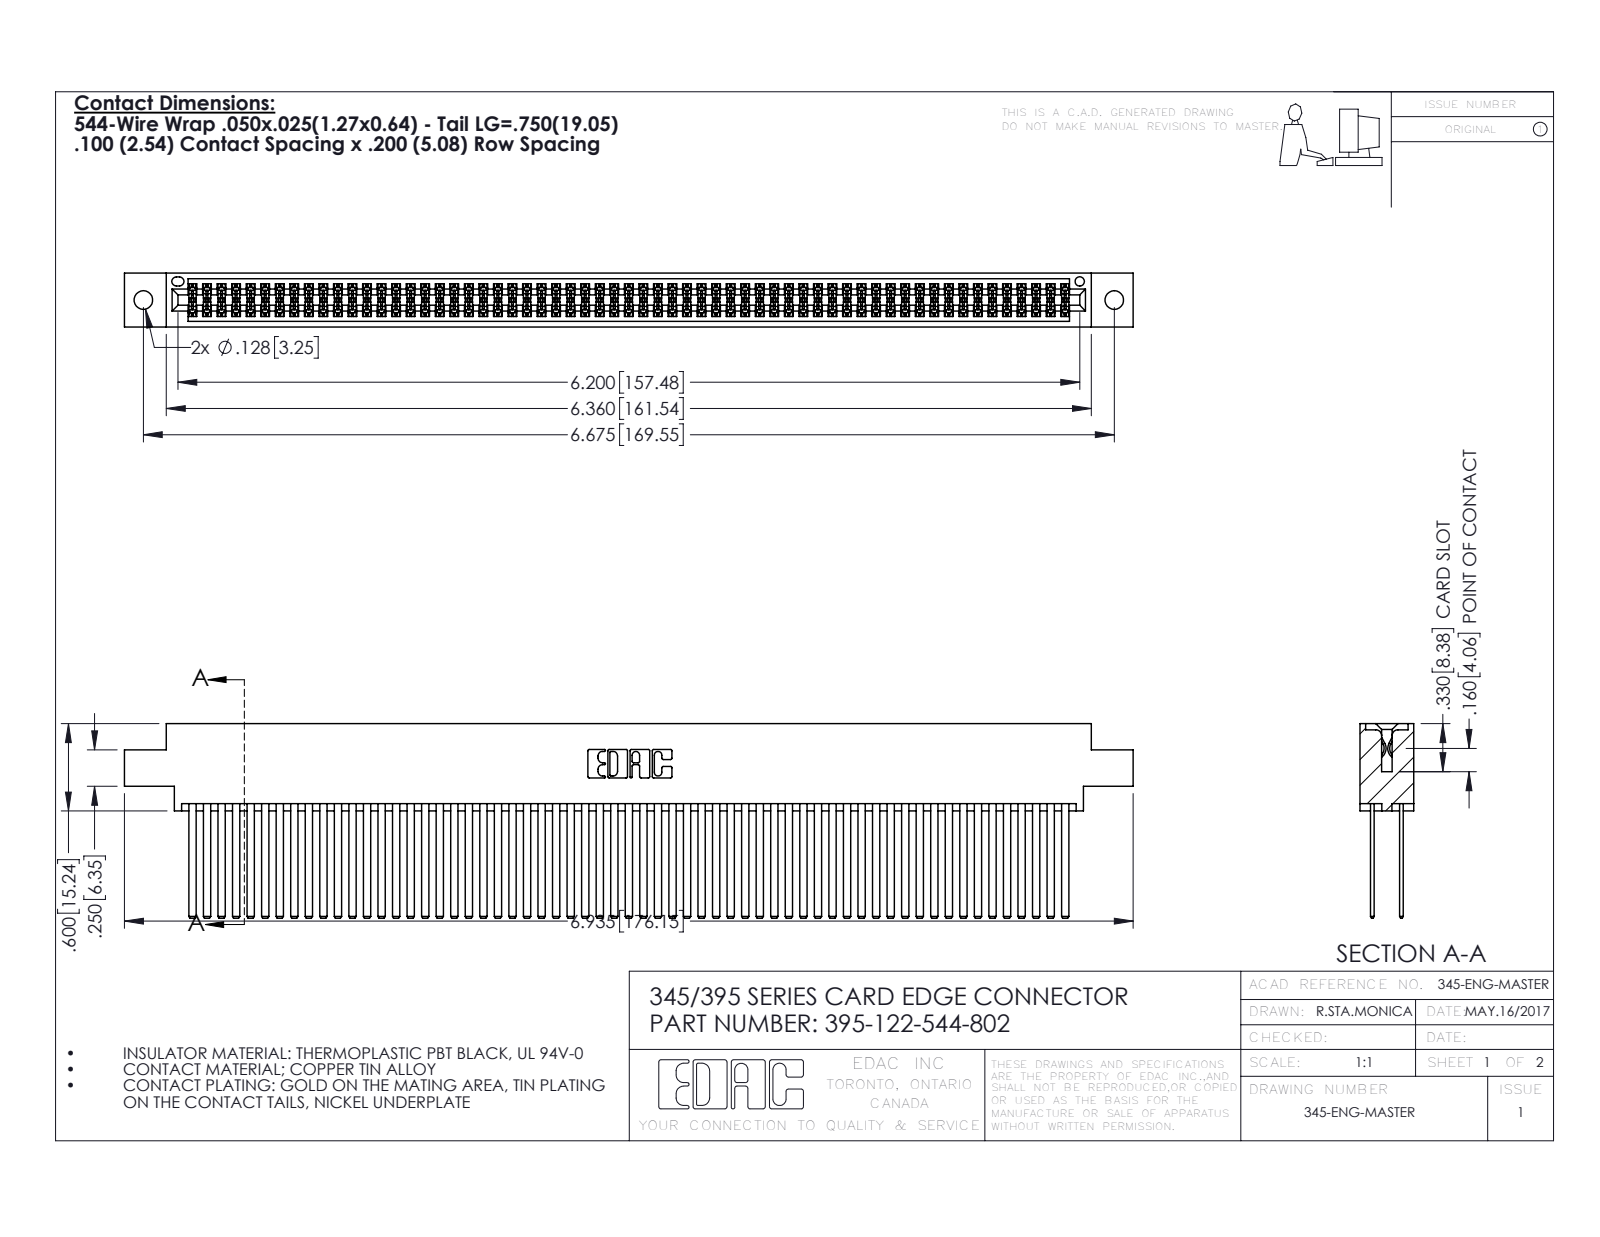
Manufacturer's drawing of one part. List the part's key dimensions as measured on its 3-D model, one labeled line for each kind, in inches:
Part name (STEP PRODUCT): 345-292-001_345-293-144; 345 Part_0.170 Offset - 0.128 Dia; 395-122-544-802
STEP written by: SolidWorks 2016 (CONFIG_CONTROL_DESIGN)
Units: inches
Bodies: 123 solids, 5498 faces (3622 planar, 1876 cylindrical, 0 other)
Overall size (bounding box): 6.935 × 1.337 × 0.37
Volume: 1.15 in³ · Surface area: 51.32 in²
Round holes (diameter × count): ⌀0.128 ×2, ⌀0.064 ×1
Partial cylindrical surfaces — rounded edges, fillets, slot ends (radius × count): R0.006 ×183, R0.01 ×22, R0.007 ×6, R0.031 ×6, R0.026 ×3, R0.014 ×2, R0.019 ×2, R0.022 ×2
Main face-to-face distances: 0.2, 0.025, 0.298, 0.072, 0.098, 0.272, 0.225, 0.175, 0.37, 0.15
Hole centre spacings: 0.27, 6.439, 6.675
